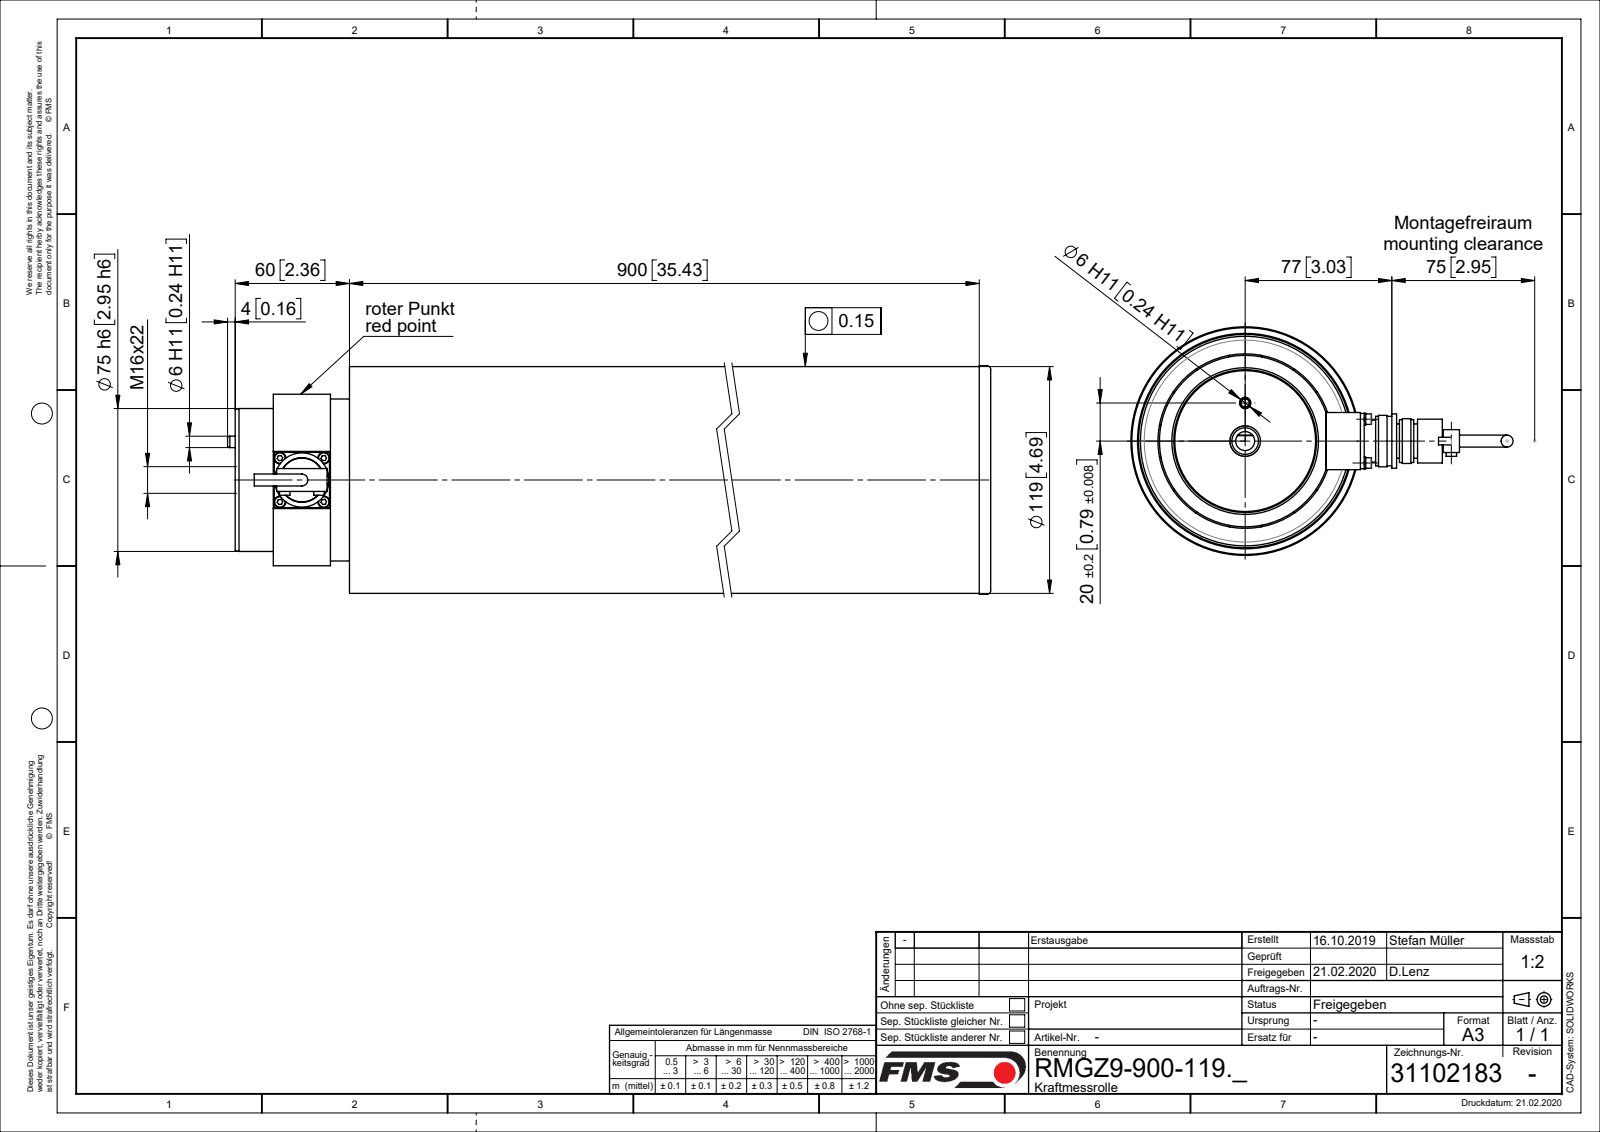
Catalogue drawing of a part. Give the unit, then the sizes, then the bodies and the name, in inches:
Units: inches
Overall size (bounding box): 38.189 × 7.9 × 4.724
Round holes (diameter × count): ⌀0.098 ×4, ⌀0.122 ×4, ⌀0.134 ×4, ⌀0.197 ×1, ⌀0.236 ×1, ⌀0.394 ×1, ⌀0.472 ×1, ⌀0.551 ×1, ⌀0.866 ×1, ⌀0.906 ×1, ⌀1.024 ×1, ⌀1.575 ×1
Round bosses / shafts (diameter × count): ⌀0.217 ×6, ⌀0.244 ×4, ⌀0.118 ×4, ⌀0.098 ×4, ⌀4.724 ×1, ⌀4.685 ×1, ⌀4.173 ×1, ⌀3.543 ×1
Partial cylindrical surfaces — rounded edges, fillets, slot ends (radius × count): R0.433 ×4, R0.167 ×2, R1.083 ×1
Main face-to-face distances: 0.079, 1.969, 1.063, 5.866, 0.236, 27.992, 0.787, 0.394, 28.071, 1.378
Hole centre spacings: 0.64, 0.906, 1.281, 0.787
Volume: 201.9 in³ · Surface area: 1 564 in²
Bodies: 37 solids, 544 faces (154 planar, 214 cylindrical, 176 other)
Part name (STEP PRODUCT): Spannstift_ISO13337_D06x12; 47726-04_stp_01; 49026_01; 47866_01 (+8 more)
STEP written by: SolidWorks 2018 (CONFIG_CONTROL_DESIGN)
